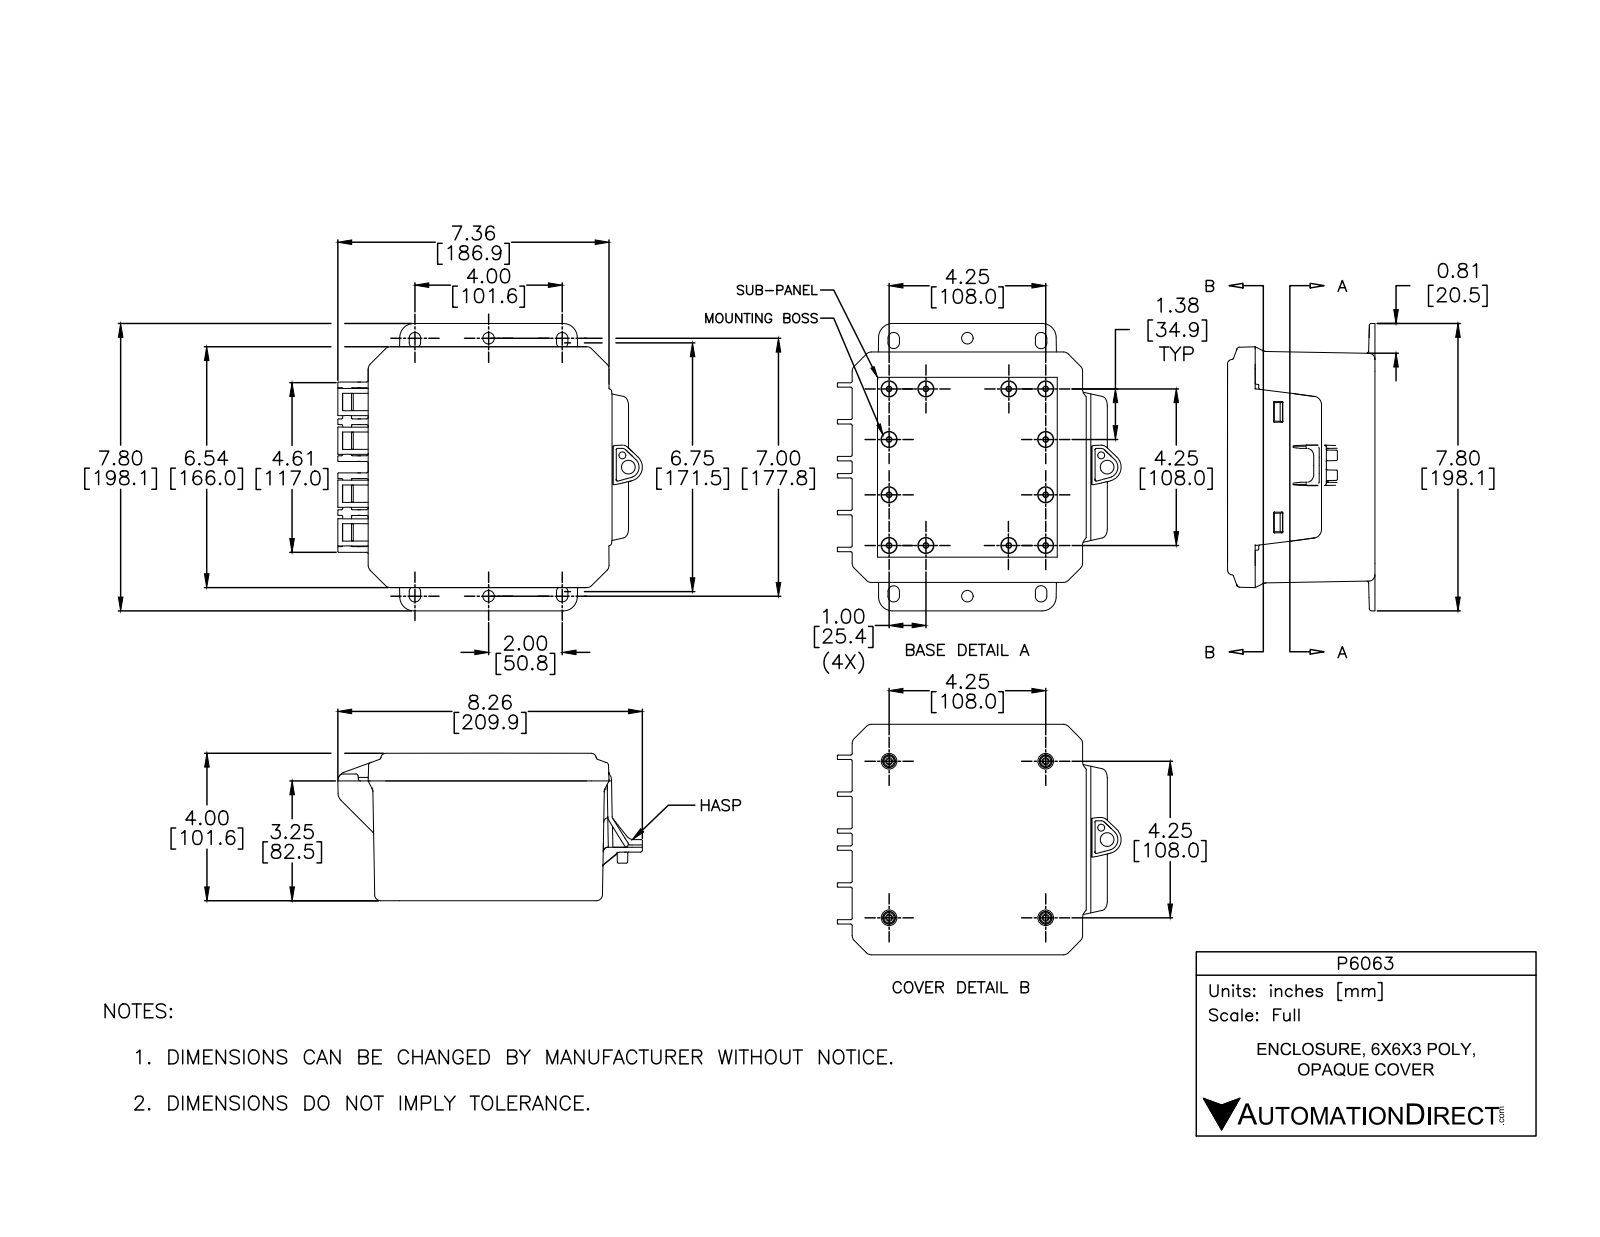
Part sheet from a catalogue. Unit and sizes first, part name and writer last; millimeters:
Units: millimetres
Overall size (bounding box): 210 × 198.1 × 101.7
Round holes (diameter × count): ⌀3.6 ×12, ⌀3 ×1
Round bosses / shafts (diameter × count): ⌀6.1 ×1
Partial cylindrical surfaces — rounded edges, fillets, slot ends (radius × count): R0.5 ×123, R0.8 ×118, R0.4 ×63, R1 ×54, R1.5 ×32, R0.3 ×31, R4.8 ×17, R2 ×12
Main face-to-face distances: 3.8, 145.1, 12, 161.6, 157.8, 157.1, 9.5, 82.6, 78.7, 25.4
Hole centre spacings: 108, 25.4, 34.9, 43.2, 73, 77.3, 82.6, 89.6
Volume: 175 500 mm³ · Surface area: 285 500 mm²
Bodies: 1 solid, 2300 faces (581 planar, 810 cylindrical, 909 other)
Part name (STEP PRODUCT): P6063; 6X6X3-LID-SD-HINGE-INT-LATCH; 6X6X3-BOX-SD-HINGE-INT-LATCH
STEP written by: SolidWorks 2016 (AUTOMOTIVE_DESIGN)
